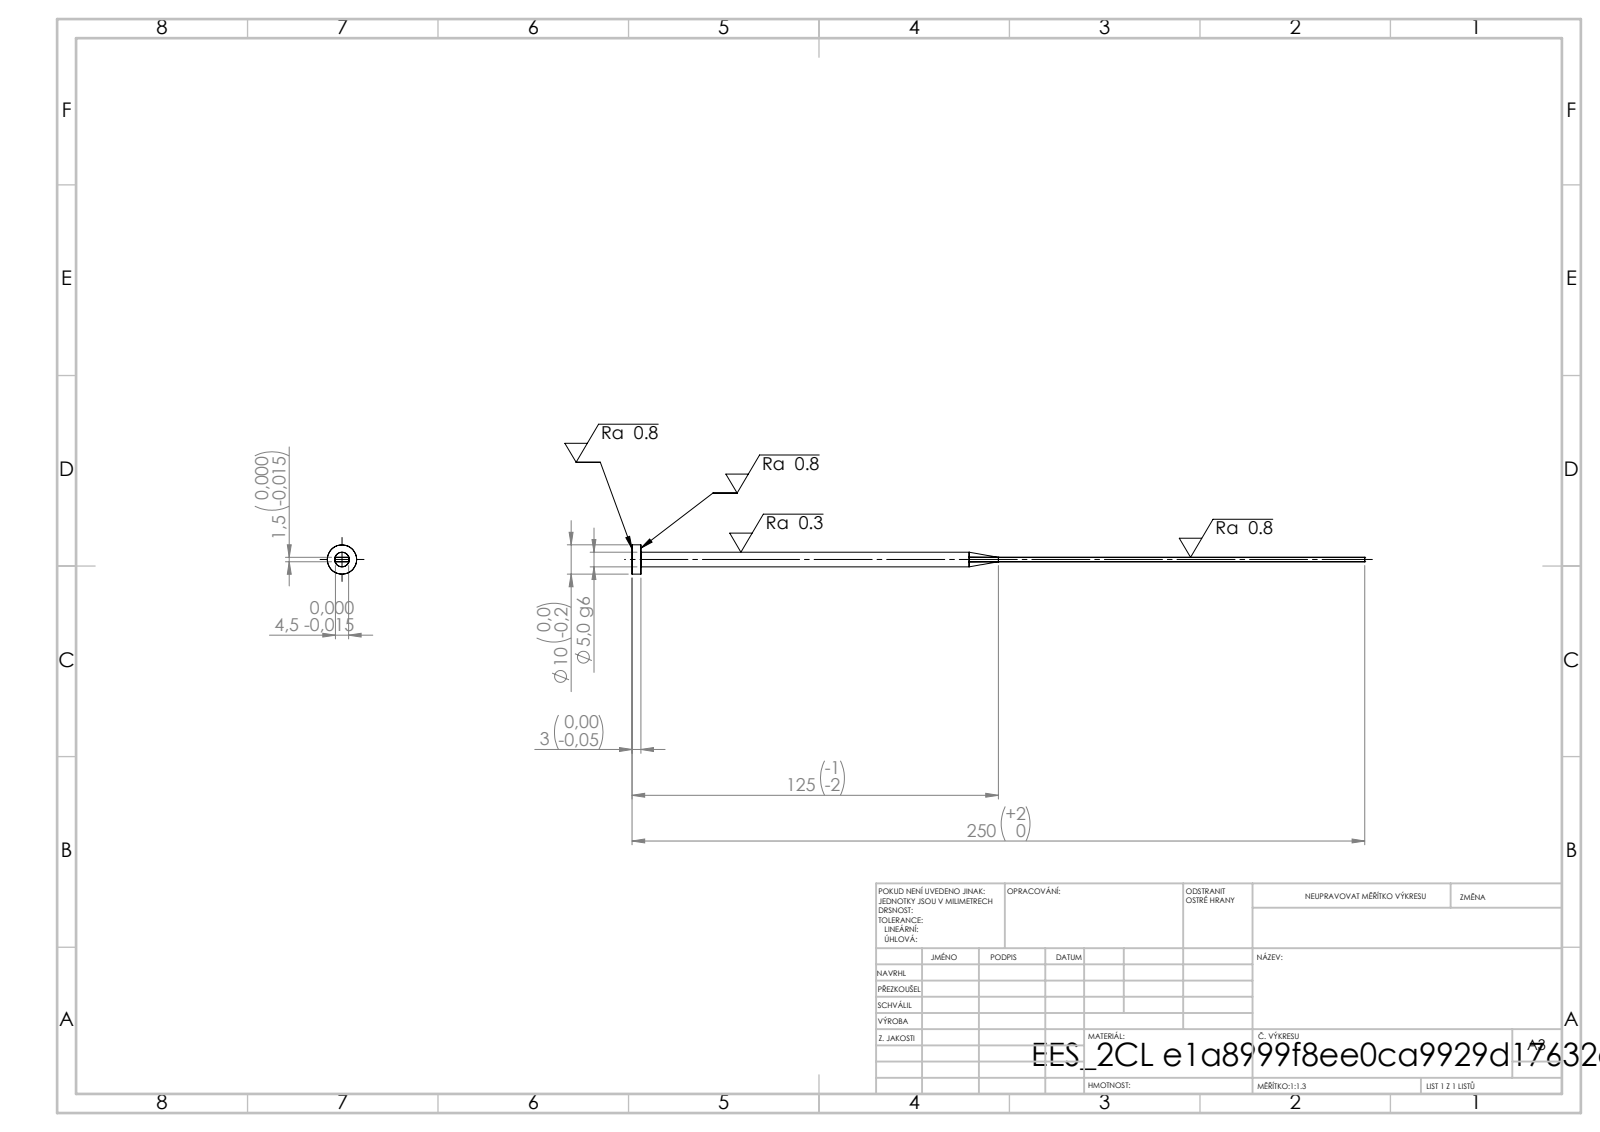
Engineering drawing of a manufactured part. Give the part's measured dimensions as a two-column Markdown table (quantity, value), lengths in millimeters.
| quantity | value |
| --- | --- |
| STEP written by | SolidWorks 2019 (CONFIG_CONTROL_DESIGN) |
| units | millimeters |
| bodies | 1 solid, 15 faces (7 planar, 4 cylindrical, 4 other) |
| overall size | 250 × 10 × 10 |
| volume | 3 406 mm³ |
| surface area | 3 632 mm² |
| round bosses / shafts (diameter × count) | 10 × 1, 5 × 1 |
| main face-to-face distances | 1.5, 4.5, 3, 250, 247 |
